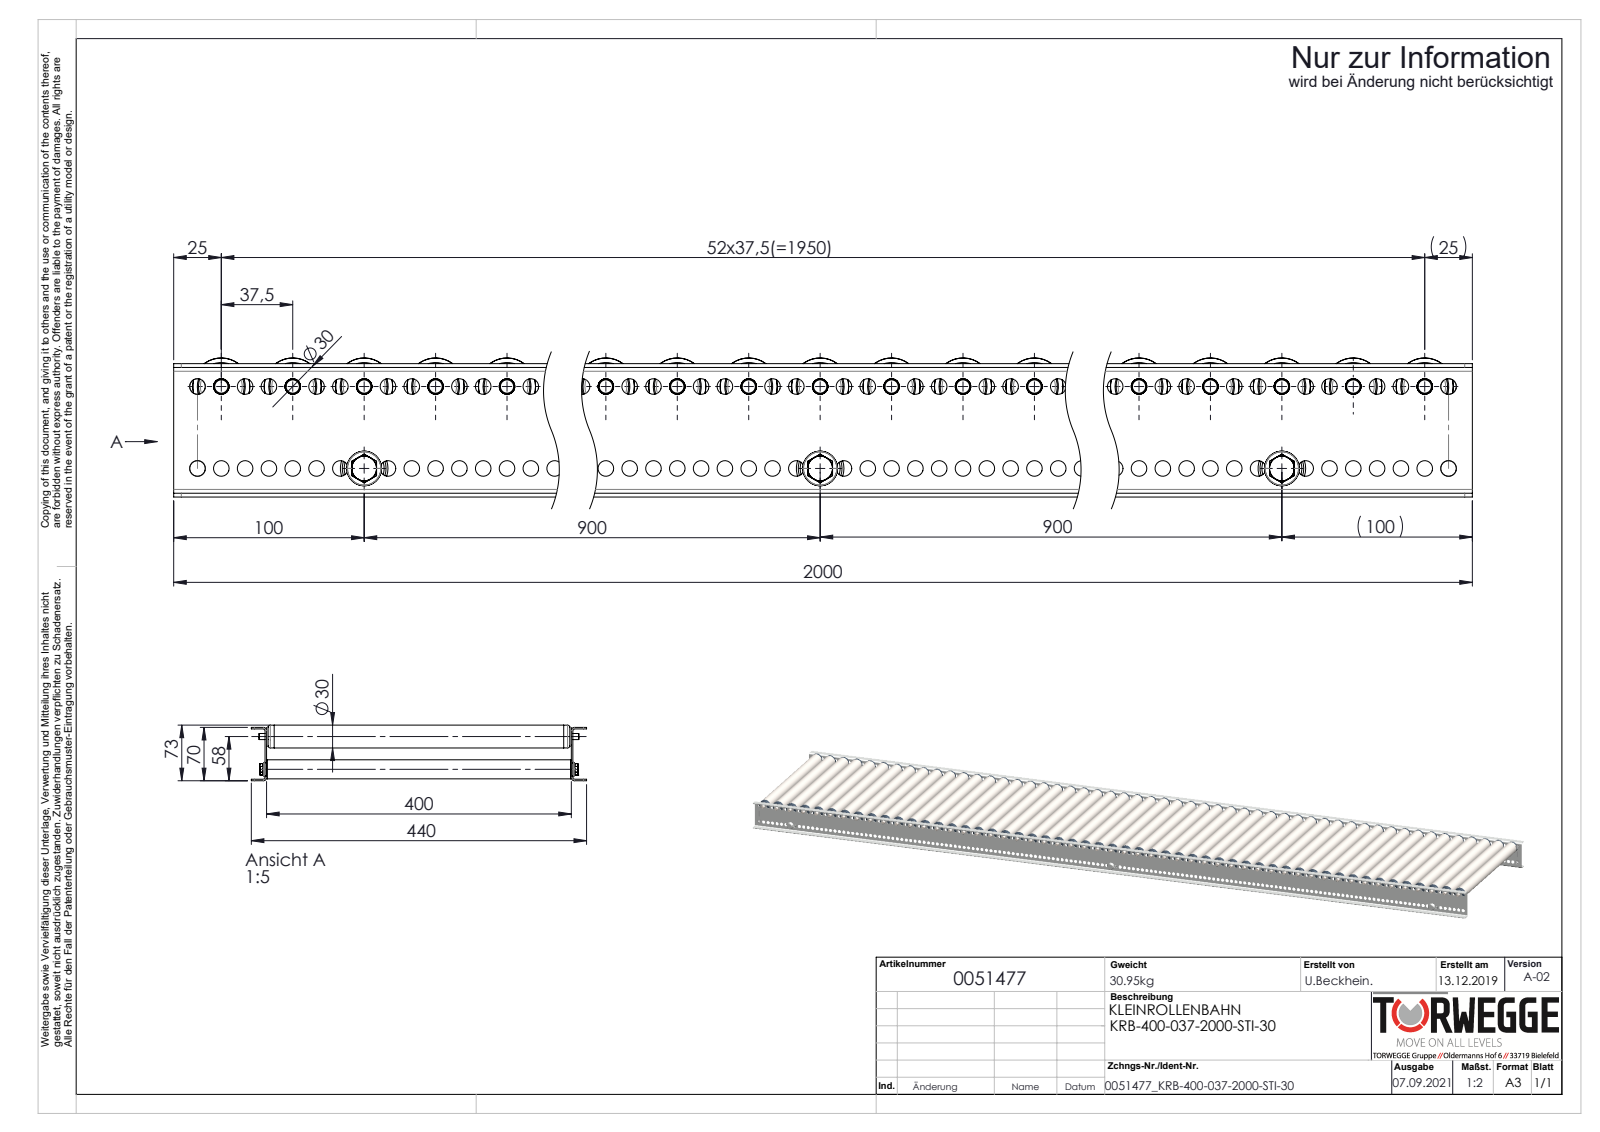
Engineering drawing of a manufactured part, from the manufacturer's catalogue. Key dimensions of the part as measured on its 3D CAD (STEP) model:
Part name (STEP PRODUCT): Profil_KRB-20x70x20x2_KFG_S100232_U-PROFIL-20-70-20-2-KRB-30-L=2000; 0042503_Typ-KUT50-30x1,5-A8; KUT50-30x1,5-STI-A8-FA_KFG_S100905_KUT50-30x1,5-STI-A8-FA-EL=400; Traversen_KFG_L400 (+6 more)
STEP written by: SolidWorks 2020 (AUTOMOTIVE_DESIGN)
Units: millimetres
Bodies: 335 solids, 14068 faces (4402 planar, 5588 cylindrical, 4078 other)
Overall size (bounding box): 2000 × 440 × 73
Volume: 4 832 000 mm³ · Surface area: 5 933 000 mm²
Round holes (diameter × count): ⌀8.2 ×318, ⌀8 ×53, ⌀8.1 ×53, ⌀23.2 ×53, ⌀25.2 ×53, ⌀27 ×53, ⌀6.8 ×3, ⌀21 ×3
Round bosses / shafts (diameter × count): ⌀30 ×53, ⌀29.9 ×53, ⌀27.1 ×53, ⌀26.8 ×53, ⌀24 ×53, ⌀14 ×53, ⌀25 ×3, ⌀8 ×3
Partial cylindrical surfaces — rounded edges, fillets, slot ends (radius × count): R5.05 ×53, R4 ×8, R2 ×4
Main face-to-face distances: 2, 402, 400, 68, 404, 70, 66, 10, 390, 20
Hole centre spacings: 12.5, 25, 37.5, 50, 62.5, 75, 87.5, 100
